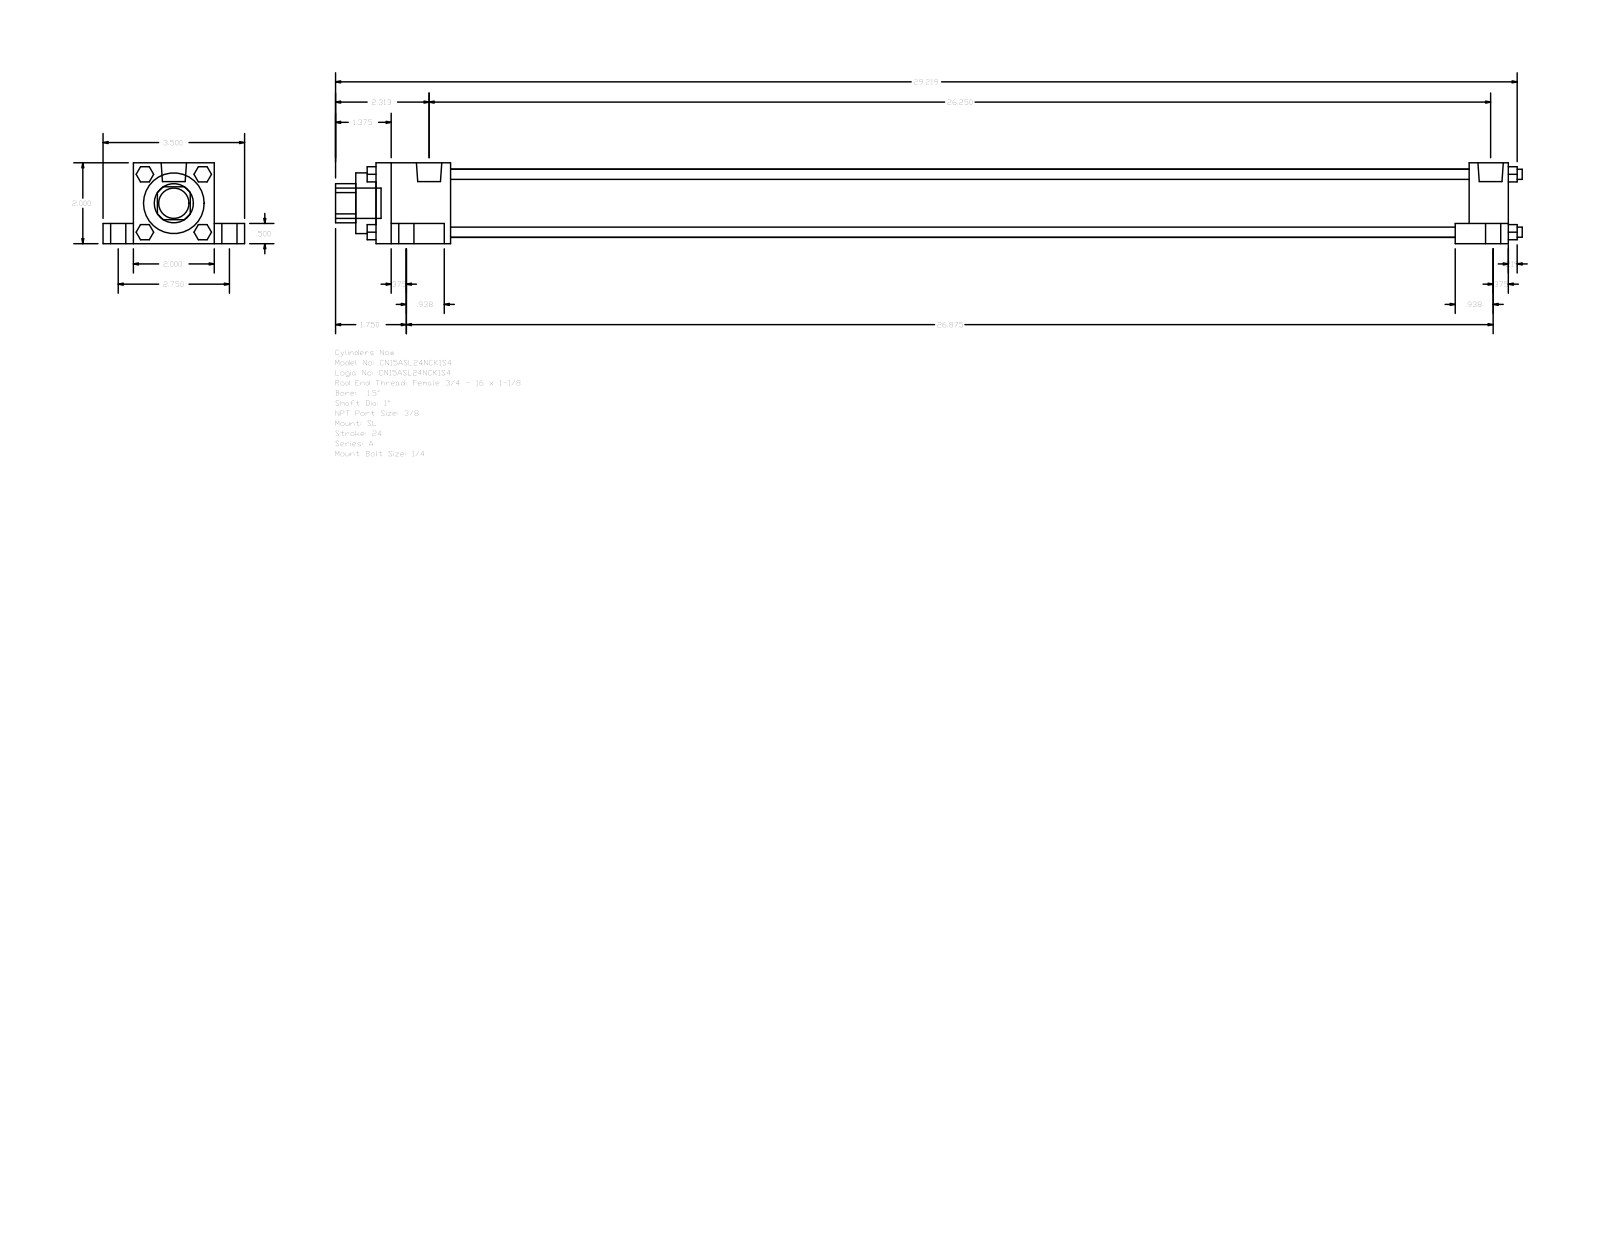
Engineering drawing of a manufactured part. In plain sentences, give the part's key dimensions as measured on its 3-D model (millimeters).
The part is named "A_SL__0150_1". Its 3-D file was written by "GSSL Pune (CONFIG_CONTROL_DESIGN)". It is 0 solids with 148 faces: 112 planar, 36 cylindrical and 0 other. Overall it measures 745.33 by 88.9 by 50.8 millimeters. Round holes: 1 of diameter 25.4, 1 of diameter 38.1, 1 of diameter 42.93. Round bosses or shafts: 4 of diameter 15.88, 4 of diameter 9.53, 4 of diameter 6.35, 4 of diameter 5.56, 2 of diameter 15.93, 1 of diameter 19.05. Partial cylindrical surfaces (rounded edges, fillets, slot ends): 1 of radius 12.29. The main face-to-face distances are 50.8, 12.7, 38.1, 19.05, 69.85, 9.52, 711.2, 33.34, 686.59, 24.61.
